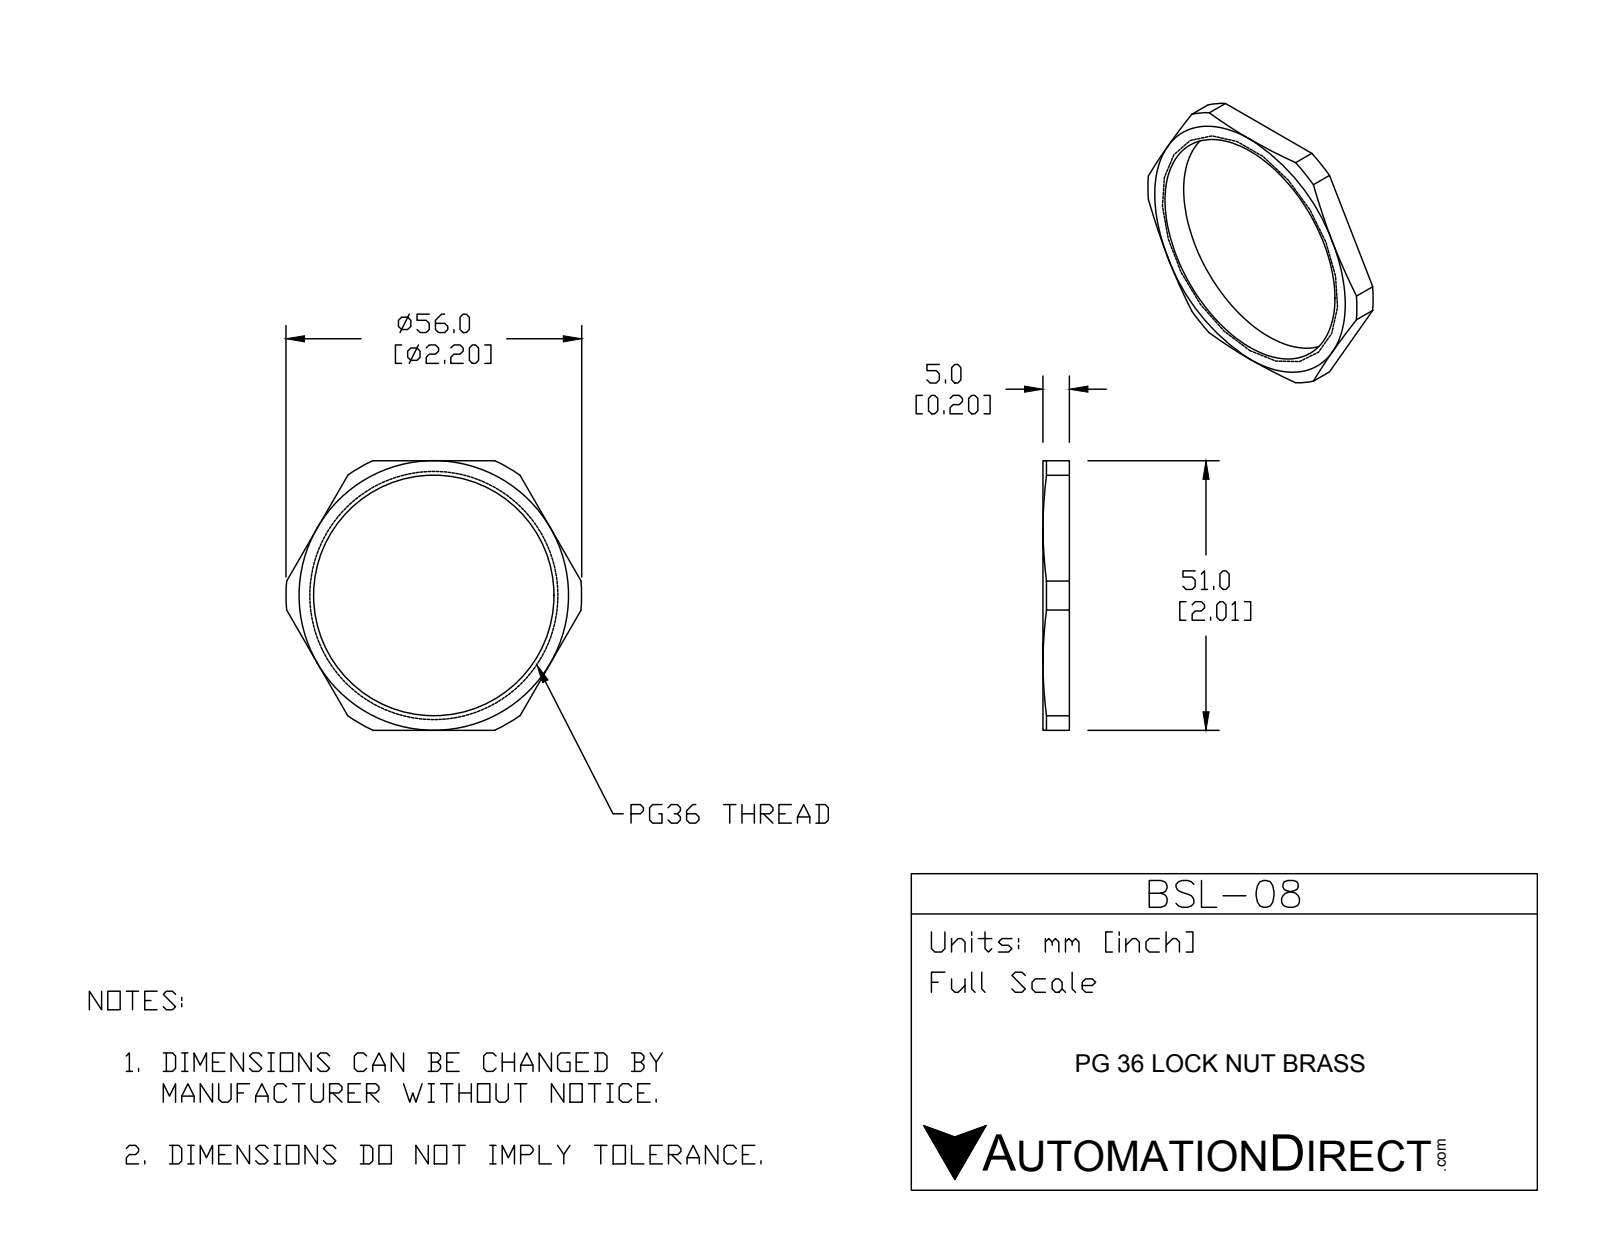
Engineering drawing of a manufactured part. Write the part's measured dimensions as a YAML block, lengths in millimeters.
part_name: "BSL-08"
step_written_by: "SolidWorks 2015 (CONFIG_CONTROL_DESIGN)"
units: millimeters
bodies: {solids: 1, faces: 23, planar: 8, cylindrical: 9, other: 6}
overall_size: [56, 51, 5]
volume: 2969
surface_area: 2733
round_holes:
  - {diameter: 45.5, count: 1}
partial_cylinders:
  - {radius: 28, count: 1}
face_to_face_distances: [5, 51]
